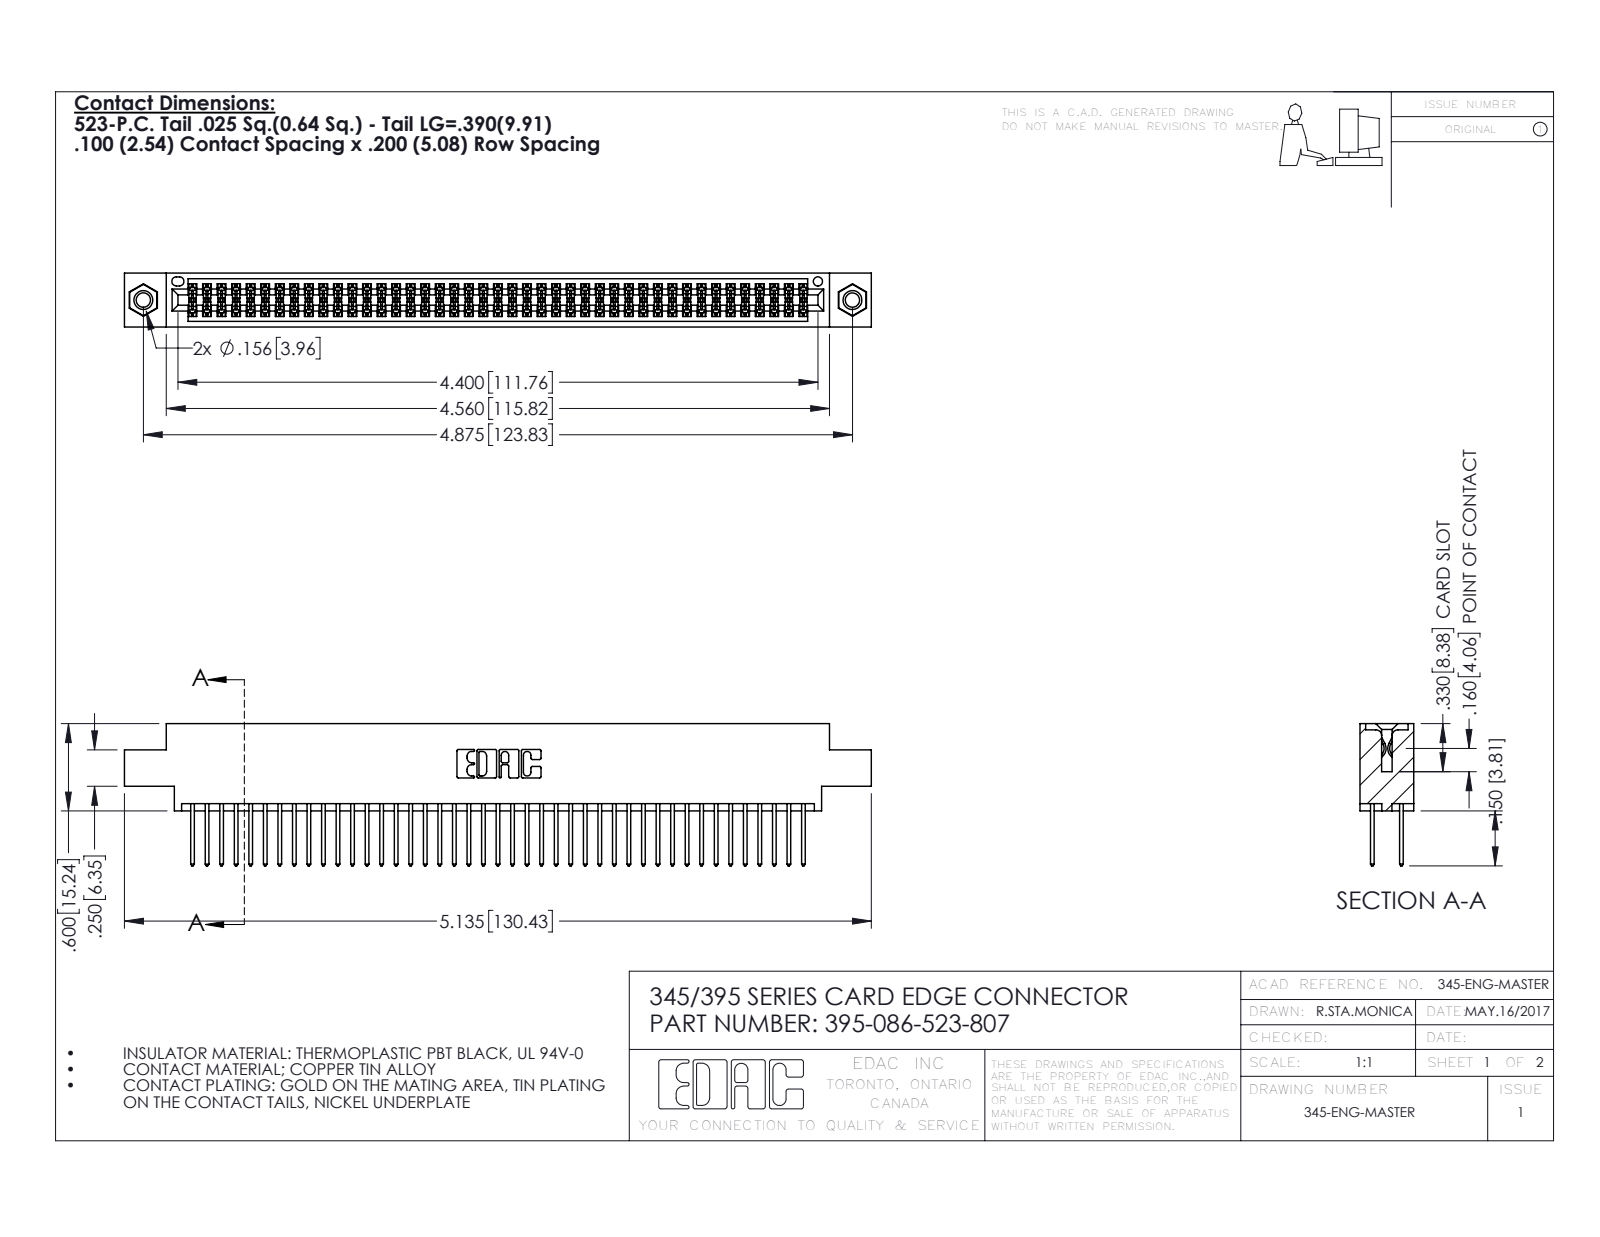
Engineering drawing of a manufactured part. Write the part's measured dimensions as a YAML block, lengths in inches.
part_name: "345-250-001_345-250-005-103; 395-086-523-807; 345 Part_0.170 Offset - 0.156 Dia-TI; 345-292-001_345-293-123"
step_written_by: "SolidWorks 2016 (CONFIG_CONTROL_DESIGN)"
units: inches
bodies: {solids: 89, faces: 4490, planar: 2954, cylindrical: 1520, other: 16}
overall_size: [5.135, 0.977, 0.37]
volume: 0.777
surface_area: 30.68
round_holes:
  - {diameter: 0.098, count: 2}
  - {diameter: 0.125, count: 2}
  - {diameter: 0.156, count: 2}
  - {diameter: 0.064, count: 1}
round_bosses_or_shafts:
  - {diameter: 0.155, count: 2}
partial_cylinders:
  - {radius: 0.006, count: 129}
  - {radius: 0.01, count: 86}
  - {radius: 0.01, count: 22}
  - {radius: 0.007, count: 6}
  - {radius: 0.031, count: 6}
  - {radius: 0.026, count: 3}
  - {radius: 0.014, count: 2}
  - {radius: 0.019, count: 2}
face_to_face_distances: [0.072, 0.298, 0.2, 0.098, 0.272, 0.025, 0.37, 0.225, 0.175, 0.149]
hole_center_spacings: [0.27, 4.639, 4.875]
